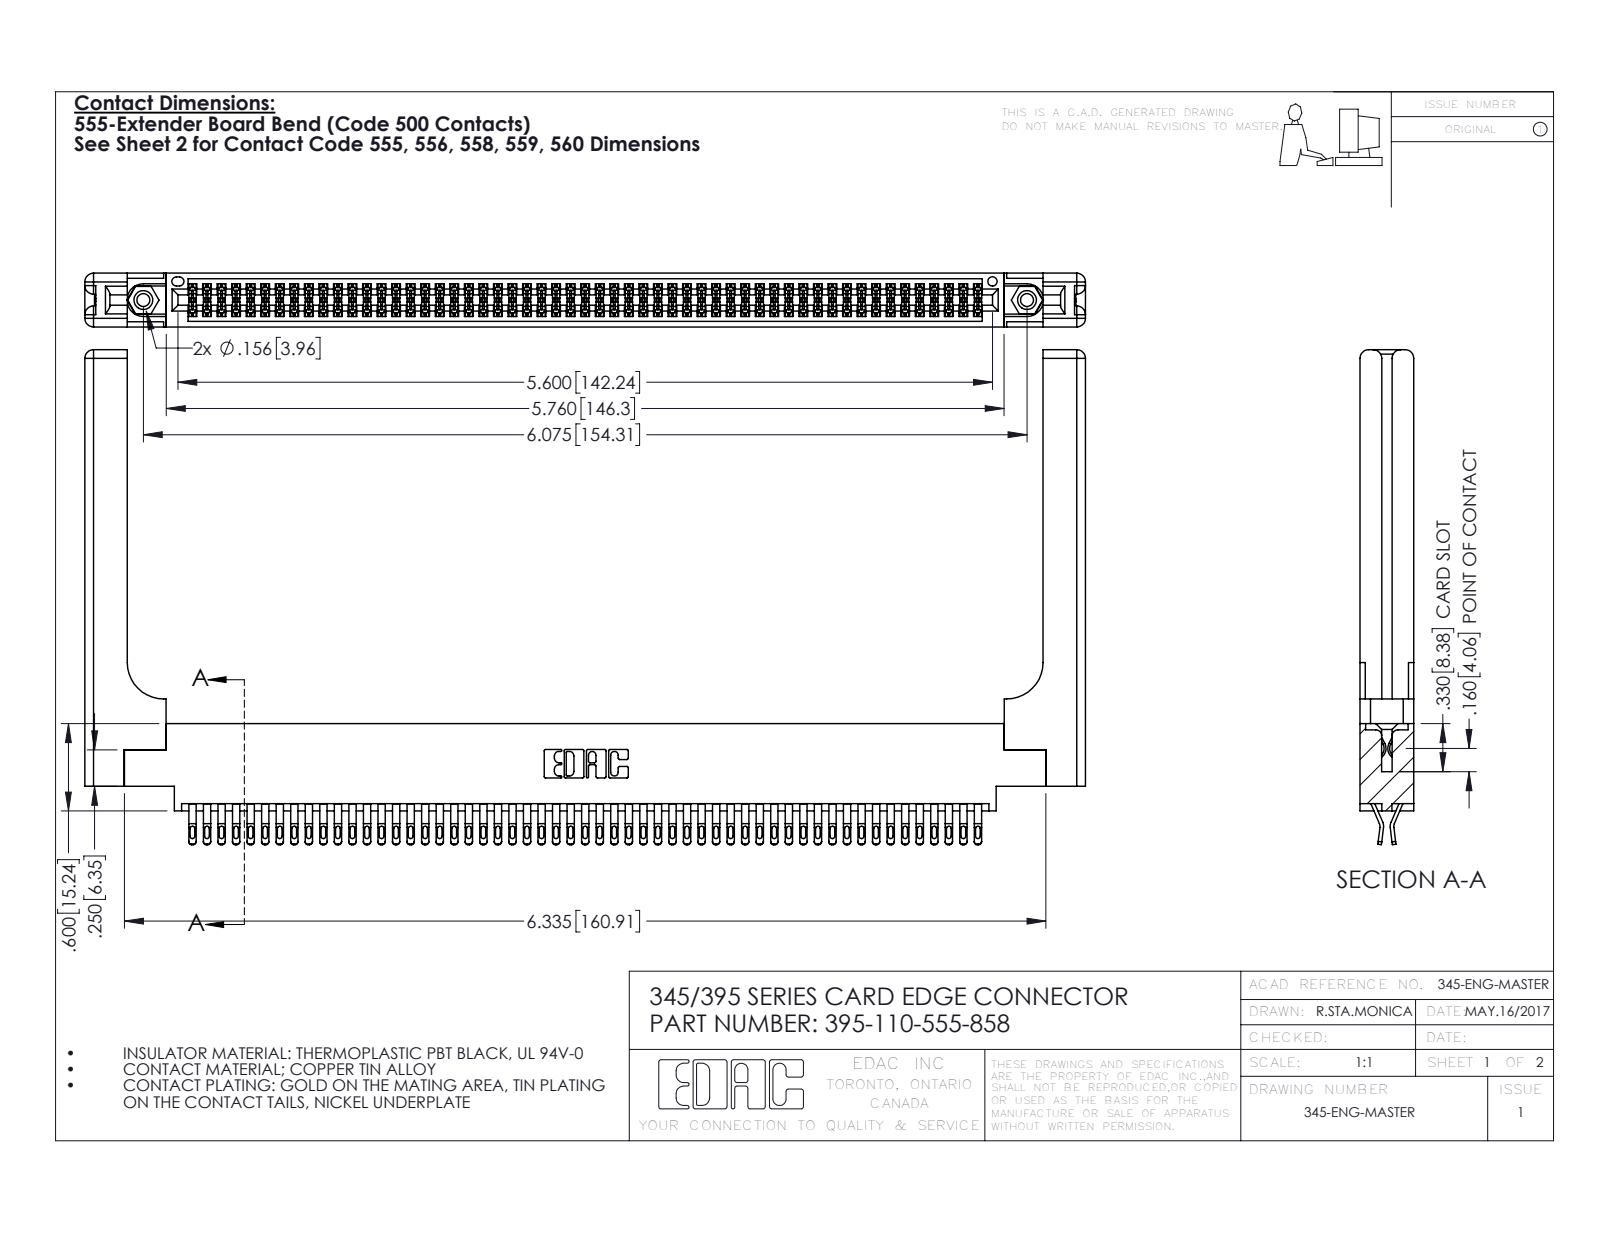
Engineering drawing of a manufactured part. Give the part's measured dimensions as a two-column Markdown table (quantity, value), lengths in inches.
| quantity | value |
| --- | --- |
| part name | 345-250-001_345-250-001-102; 345-220-058_345-220-058; 345 Part_0.170 Offset - 0.156 Dia-TH; 345-292-001_555 Tail (+1 more) |
| STEP written by | SolidWorks 2016 (CONFIG_CONTROL_DESIGN) |
| units | inches |
| bodies | 115 solids, 6546 faces (3642 planar, 2844 cylindrical, 60 other) |
| overall size | 6.879 × 3.402 × 0.37 |
| volume | 1.573 in³ |
| surface area | 49.81 in² |
| round holes (diameter × count) | 0.089 × 2, 0.125 × 2, 0.156 × 2, 0.064 × 1 |
| round bosses / shafts (diameter × count) | 0.155 × 2 |
| partial cylindrical surfaces (radius × count) | 0.016 × 275, 0.02 × 220, 0.006 × 165, 0.01 × 22, 0.06 × 16, 0.007 × 6, 0.031 × 6, 0.026 × 3 |
| main face-to-face distances | 0.072, 0.37, 0.298, 0.025, 0.098, 0.272, 0.2, 0.225, 0.175, 0.148 |
| hole center spacings | 0.27, 5.839, 6.075 |
